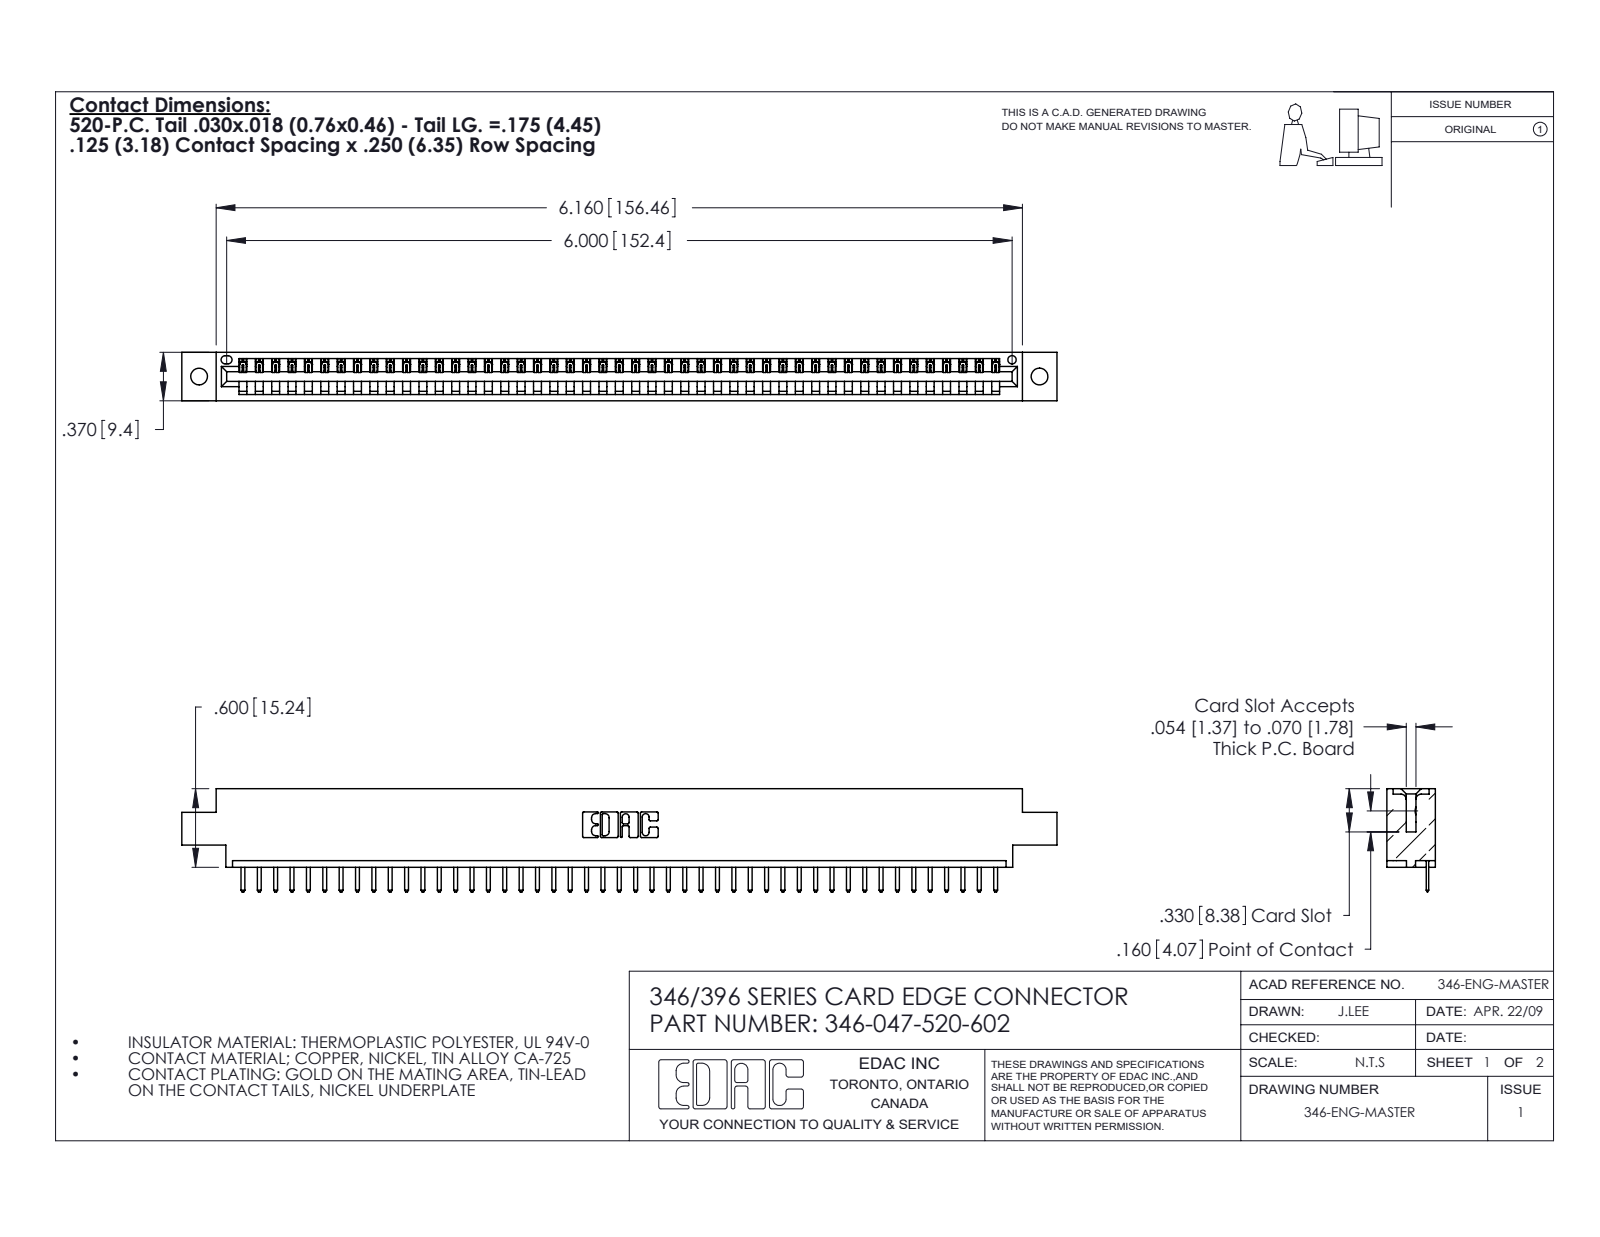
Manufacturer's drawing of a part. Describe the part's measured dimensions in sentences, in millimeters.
The part is named "346-047-520-602; 345-292-001_345-293-120; 346 Part_0.170 Offset - 0.128 Dia". Its 3-D file was written by "SolidWorks 2020 (CONFIG_CONTROL_DESIGN)". It is 48 solids with 3040 faces: 2054 planar, 986 cylindrical and 0 other. Overall it measures 169.8 by 20 by 9.4 millimeters. Its volume is 16 000 cubic millimeters and its surface area 19 440 square millimeters. Round holes: 2 of diameter 3.3, 1 of diameter 1.6. Partial cylindrical surfaces (rounded edges, fillets, slot ends): 96 of radius 0.3, 94 of radius 0.2, 22 of radius 0.3, 6 of radius 0.2, 6 of radius 0.8, 3 of radius 0.7, 2 of radius 0.8, 2 of radius 1. The main face-to-face distances are 1.2, 8.2, 9.4, 6.4, 3.8, 5.6, 2.5, 4.4, 1.8, 7.6. The hole center spacings are 6.2, 157.8, 163.1.
